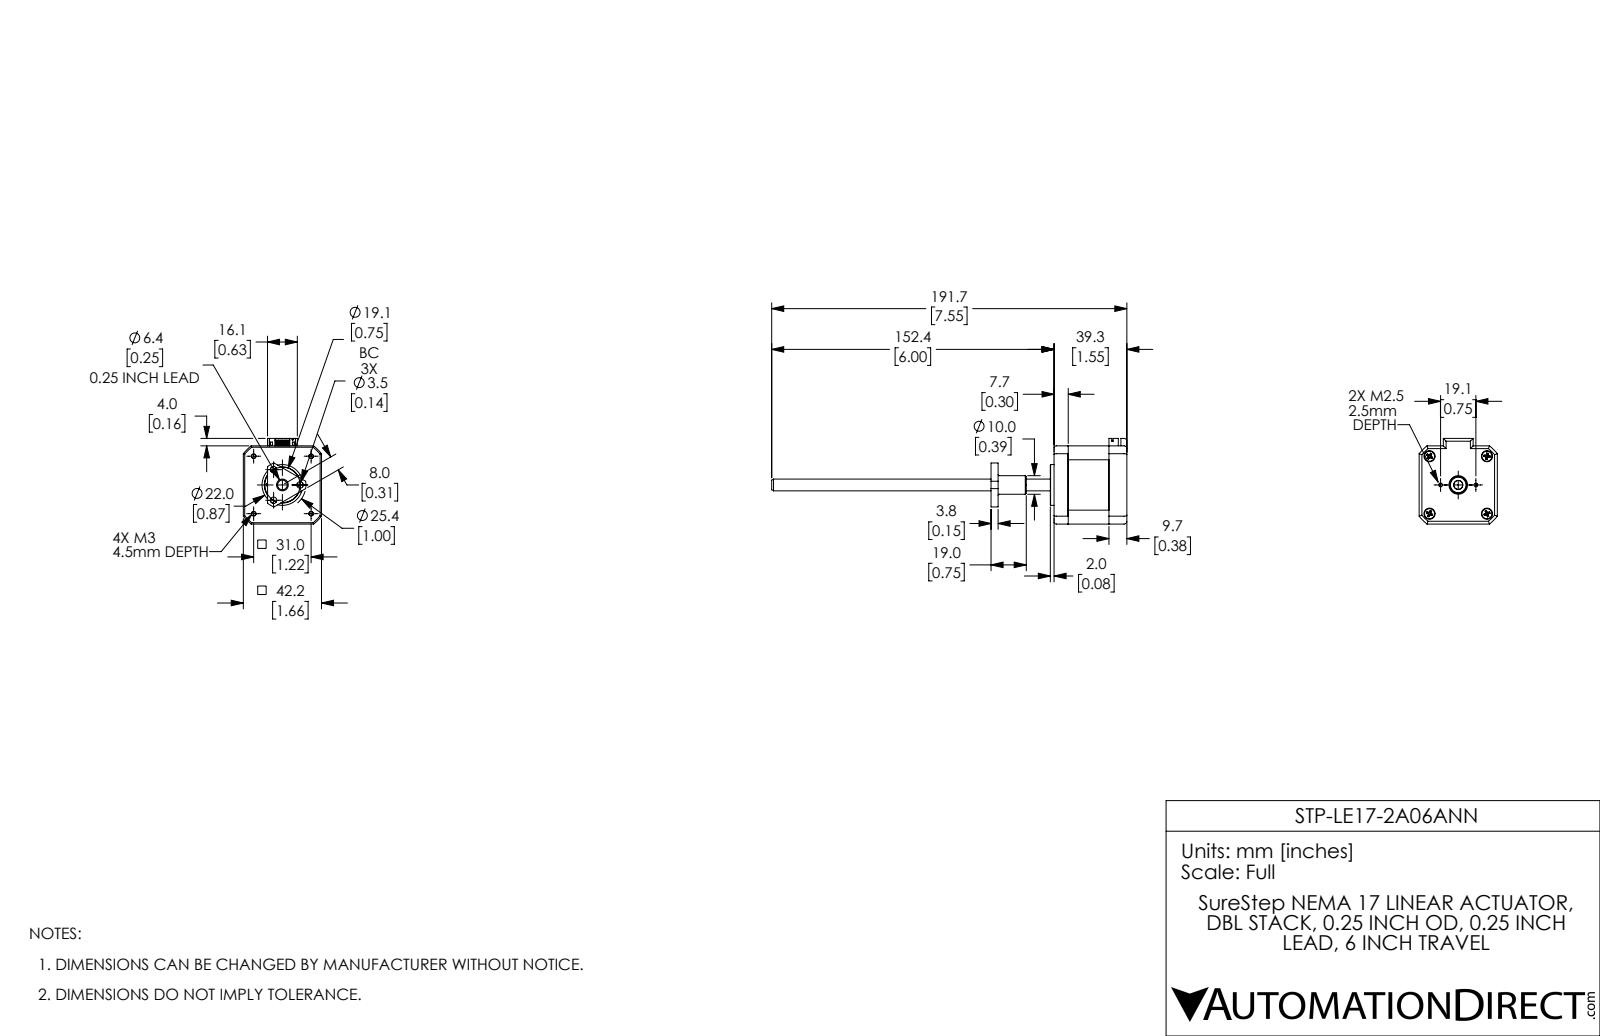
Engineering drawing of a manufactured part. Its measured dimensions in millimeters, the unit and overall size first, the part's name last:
Units: millimetres
Overall size (bounding box): 191.7 × 46.2 × 42.2
Round holes (diameter × count): ⌀2.5 ×4, ⌀3.8 ×4, ⌀6 ×4, ⌀3.5 ×3, ⌀1.5 ×2, ⌀2.05 ×2, ⌀4.9 ×1, ⌀5 ×1, ⌀13 ×1, ⌀17 ×1, ⌀19.46 ×1, ⌀20 ×1
Round bosses / shafts (diameter × count): ⌀5.4 ×4, ⌀2.91 ×4, ⌀27 ×1, ⌀25.91 ×1, ⌀22 ×1, ⌀12 ×1, ⌀10 ×1, ⌀9 ×1
Partial cylindrical surfaces — rounded edges, fillets, slot ends (radius × count): R1 ×12, R1.5 ×11, R2.5 ×2, R0.7 ×1, R12.7 ×1, R14.25 ×1, R16 ×1, R25.1 ×1
Main face-to-face distances: 42.2, 9.65, 39.3, 29.65, 31.65, 1.6, 22, 7.65, 1, 36.8
Hole centre spacings: 16.61, 9.52, 21.92, 29.43, 31, 4.93, 8, 12.96
Volume: 63 935 mm³ · Surface area: 28 167 mm²
Bodies: 6 solids, 726 faces (360 planar, 232 cylindrical, 134 other)
Part name (STEP PRODUCT): STP-LE17-2A06ANN_2; STP-LE17-2A06ANN_1; STP-LE17-2A06ANN
STEP written by: SolidWorks 2017 (AUTOMOTIVE_DESIGN)
